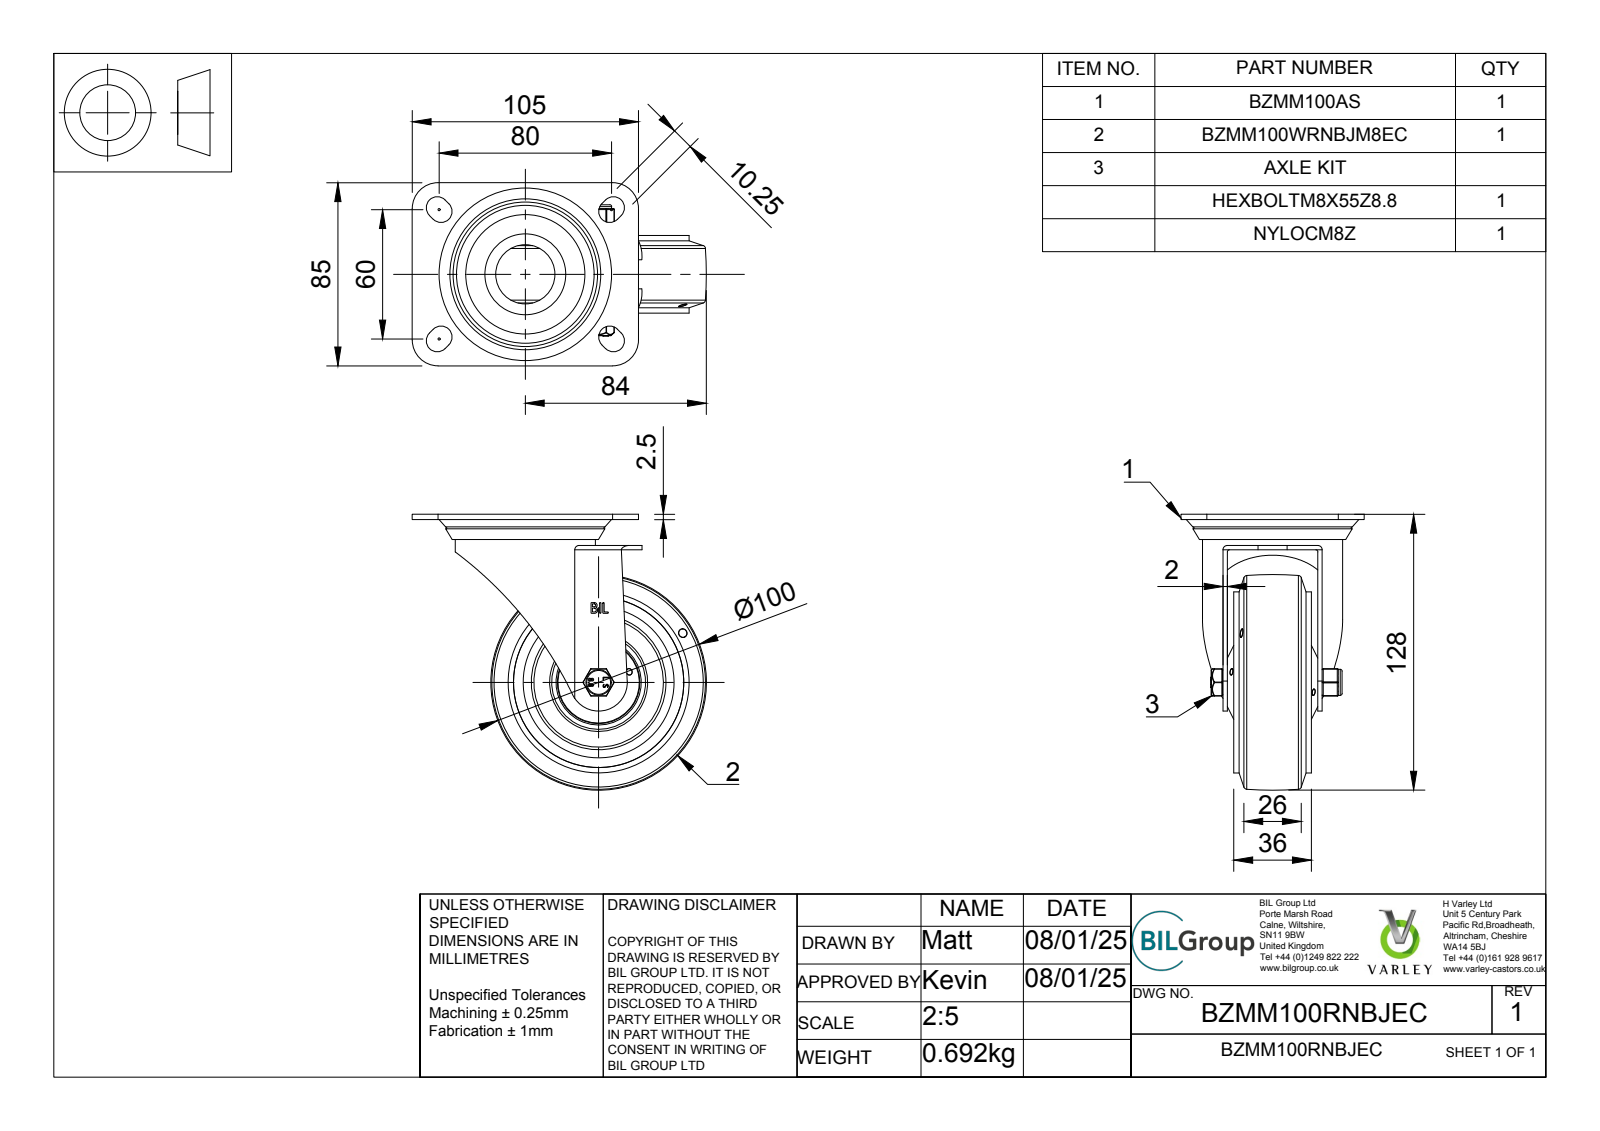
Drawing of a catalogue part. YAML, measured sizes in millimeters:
part_name: "BZMM100RNBJEC v4; BZMM100AS - 2 - 42 v1; ZINC PLATED, PRESSED STEEL TOP PLATE; ZINC PLATED, PRESSED STEEL TOP PLATE Geometry (+7 more)"
step_written_by: "Autodesk Translation Framework v13.20.0.188 (AP242_MANAGED_MODEL_BASED_3D_ENGINEERING_MIM_LF)"
units: millimeters
bodies: {solids: 50, faces: 775, planar: 277, cylindrical: 199, other: 299}
overall_size: [136.5, 128, 85]
volume: 243394
surface_area: 129836
round_holes:
  - {diameter: 0.66, count: 2}
  - {diameter: 3, count: 2}
  - {diameter: 4, count: 1}
  - {diameter: 8, count: 1}
  - {diameter: 8.2, count: 1}
  - {diameter: 8.25, count: 1}
  - {diameter: 8.6, count: 1}
  - {diameter: 15, count: 1}
  - {diameter: 20, count: 1}
  - {diameter: 22.5, count: 1}
  - {diameter: 26, count: 1}
  - {diameter: 27.5, count: 1}
round_bosses_or_shafts:
  - {diameter: 84, count: 1}
  - {diameter: 65, count: 1}
  - {diameter: 43.5, count: 1}
  - {diameter: 38.25, count: 1}
  - {diameter: 34.5, count: 1}
  - {diameter: 31.5, count: 1}
  - {diameter: 30.5, count: 1}
  - {diameter: 28, count: 1}
partial_cylinders:
  - {radius: 0.5, count: 18}
  - {radius: 0.25, count: 12}
  - {radius: 5.12, count: 8}
  - {radius: 12, count: 5}
  - {radius: 0.33, count: 4}
  - {radius: 0.64, count: 4}
  - {radius: 1, count: 4}
  - {radius: 0.63, count: 2}
face_to_face_distances: [2, 5, 39, 3, 2.5, 41, 44, 18.25, 25.75, 20.75]
hole_center_spacings: [3.22, 2.49]
